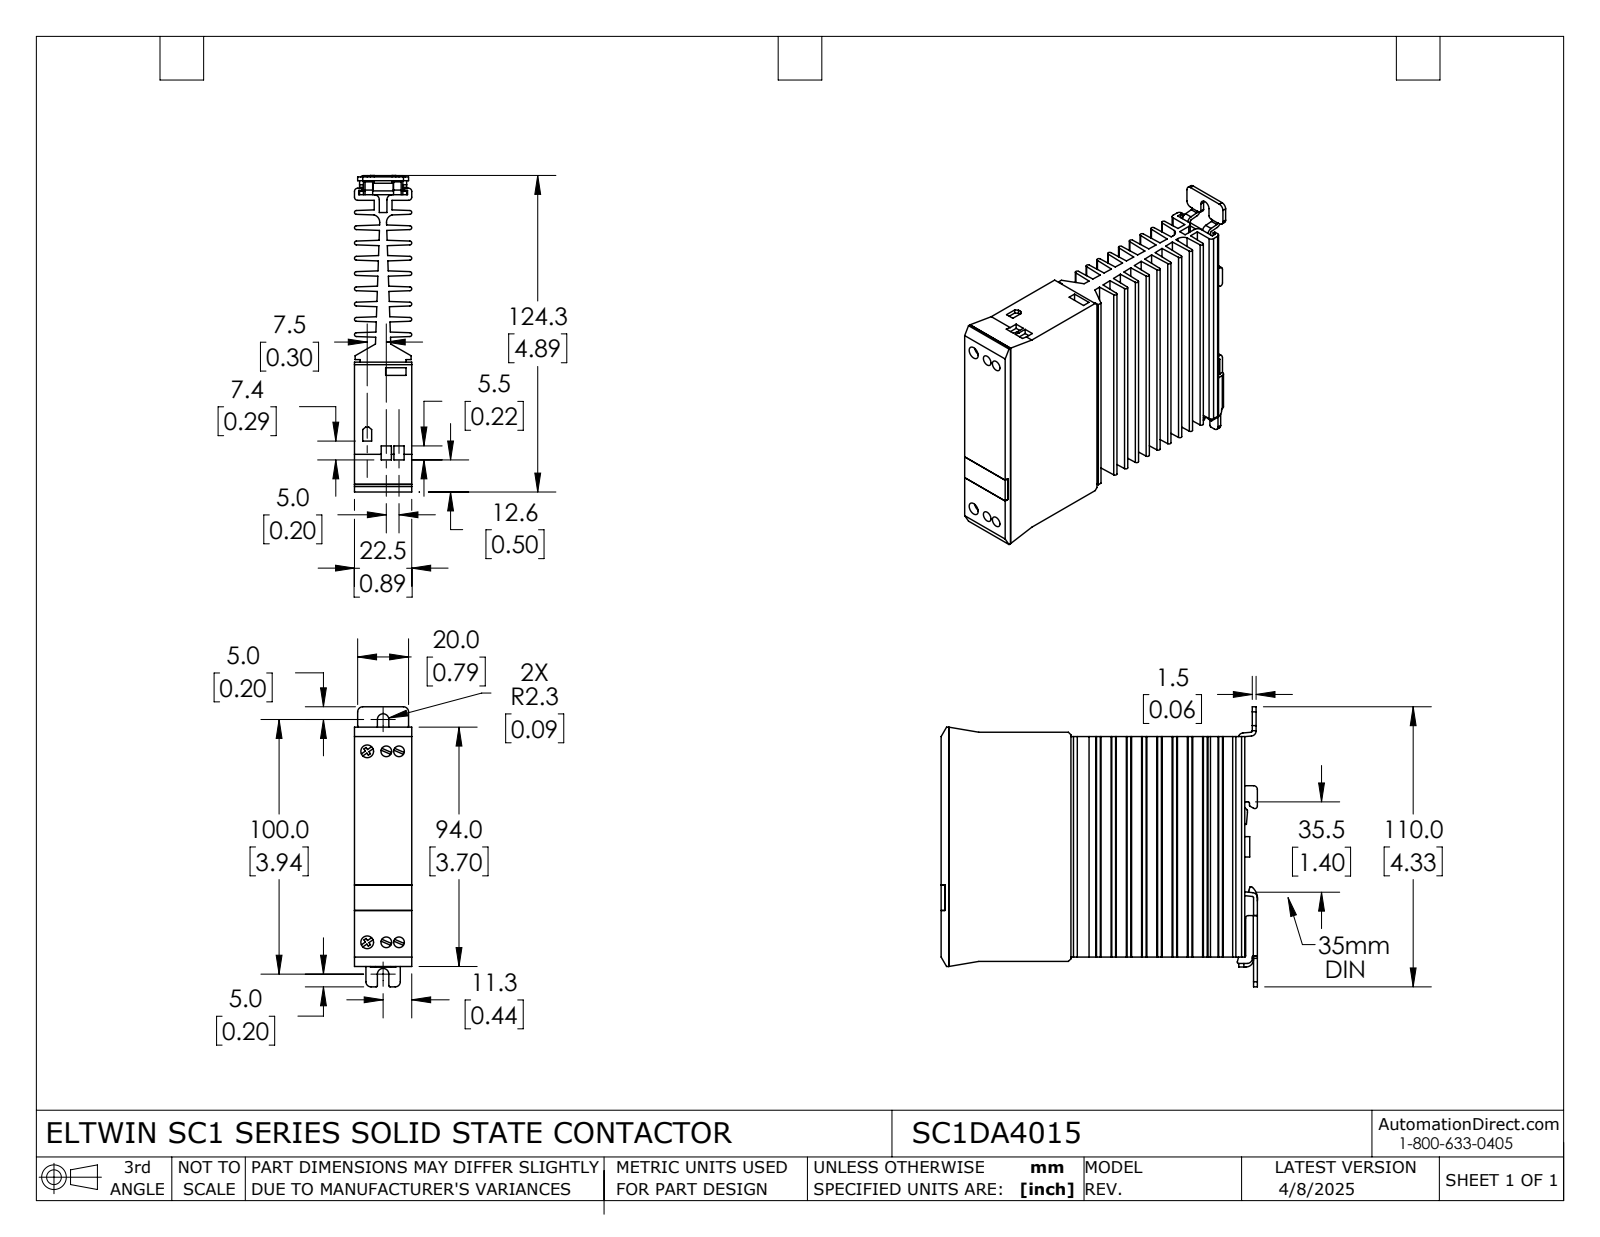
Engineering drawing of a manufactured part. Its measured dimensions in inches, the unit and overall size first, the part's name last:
Units: inches
Overall size (bounding box): 4.894 × 4.331 × 0.886
Round holes (diameter × count): ⌀0.165 ×4, ⌀0.173 ×4, ⌀0.197 ×2, ⌀0.236 ×2
Round bosses / shafts (diameter × count): ⌀0.315 ×1
Partial cylindrical surfaces — rounded edges, fillets, slot ends (radius × count): R0.02 ×29, R0.03 ×18, R0.079 ×18, R0.039 ×15, R0.059 ×5, R0.049 ×4, R0.118 ×3, R0.004 ×2
Main face-to-face distances: 0.236, 0.472, 0.708, 0.148, 0.56, 0.236, 1.18, 0.088, 0.62, 0.324
Hole centre spacings: 2.953, 0.197, 0.295, 0.492, 2.959, 2.967, 2.993
Volume: 10.14 in³ · Surface area: 115.4 in²
Bodies: 6 solids, 489 faces (326 planar, 161 cylindrical, 2 other)
Part name (STEP PRODUCT): SC1DA4015
STEP written by: SolidWorks 2021 (AUTOMOTIVE_DESIGN)
